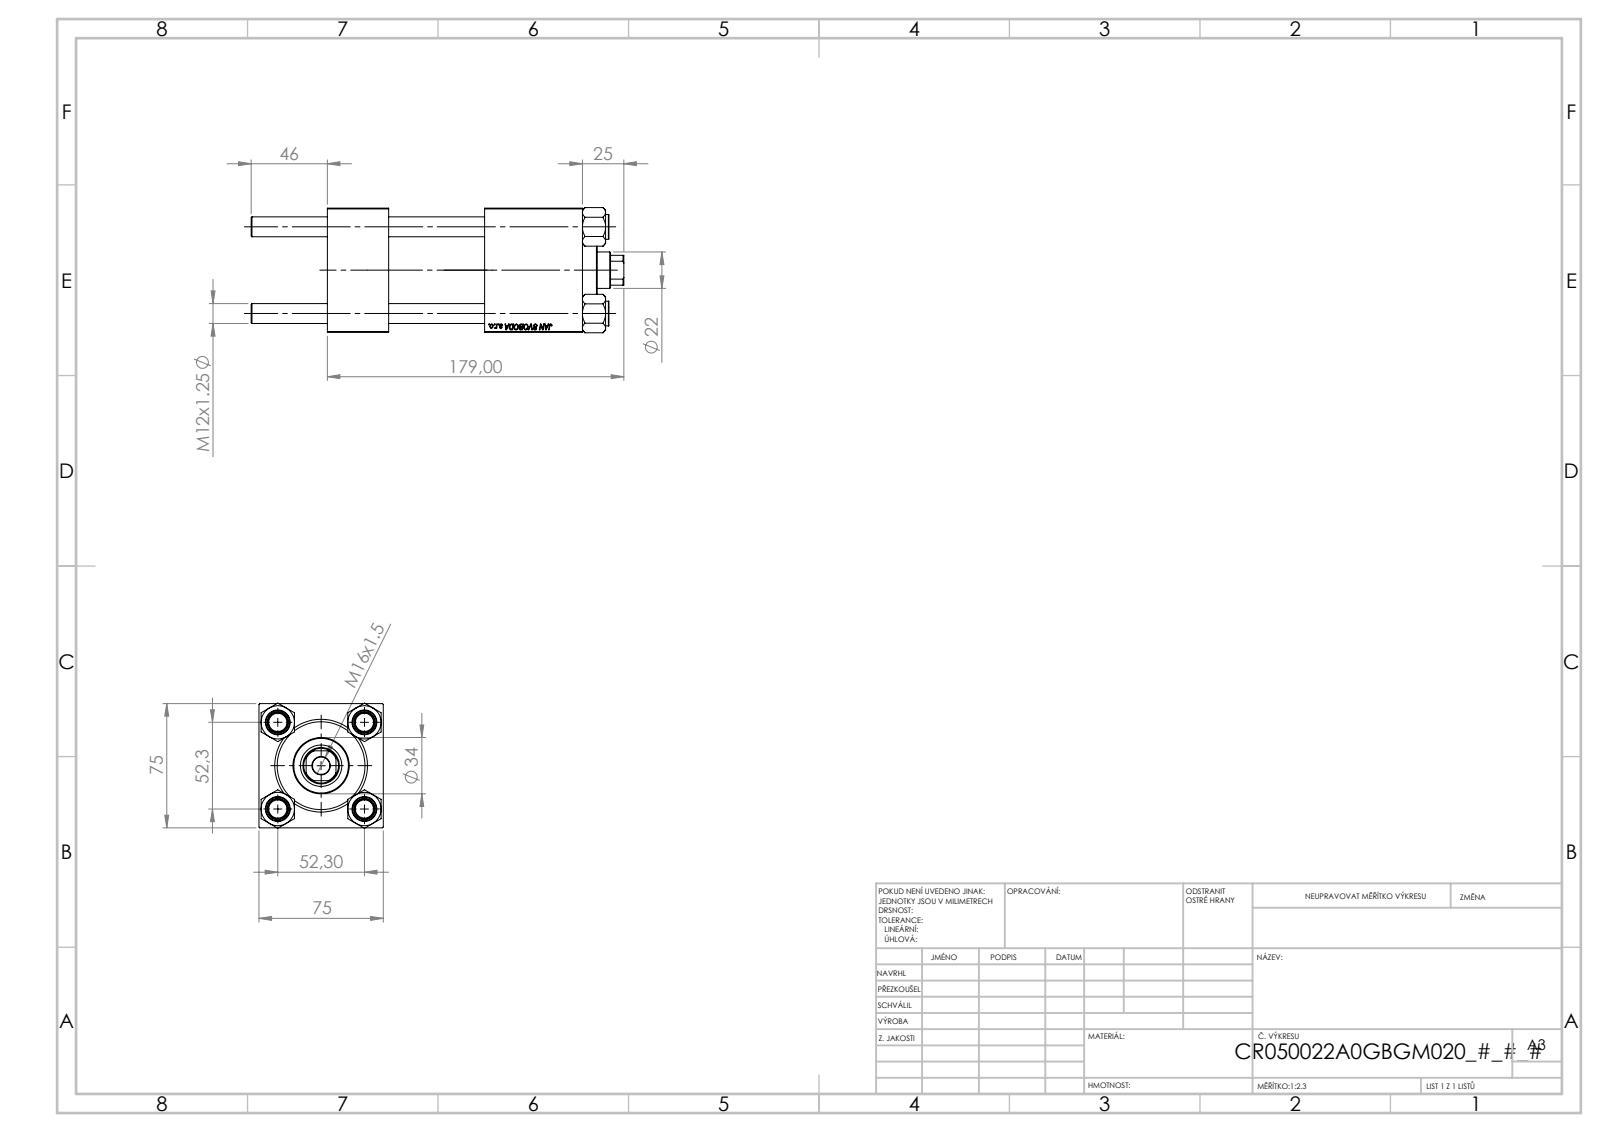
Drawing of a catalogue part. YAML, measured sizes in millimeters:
part_name: "CR025_012_A_0_G_A_G_M_020_+#_##_TYCINKA; V215CR_VCP; V215CR_BODY_A; NUT_M5 (+1 more)"
step_written_by: "SolidWorks 2019 (CONFIG_CONTROL_DESIGN)"
units: millimeters
bodies: {solids: 11, faces: 1133, planar: 519, cylindrical: 78, other: 536}
overall_size: [225, 75.54, 75]
volume: 689902
surface_area: 163881
round_holes:
  - {diameter: 12, count: 4}
  - {diameter: 7, count: 2}
  - {diameter: 20.96, count: 2}
  - {diameter: 30, count: 2}
  - {diameter: 10.5, count: 1}
  - {diameter: 22, count: 1}
  - {diameter: 25, count: 1}
  - {diameter: 41, count: 1}
  - {diameter: 50, count: 1}
  - {diameter: 53, count: 1}
round_bosses_or_shafts:
  - {diameter: 15, count: 4}
  - {diameter: 56, count: 1}
  - {diameter: 34, count: 1}
partial_cylinders:
  - {radius: 10.5, count: 1}
face_to_face_distances: [75, 37, 154, 117, 95, 58, 59, 125.3, 88.3, 30.3]
hole_center_spacings: [36.98, 52.3, 73.96, 93.5]
